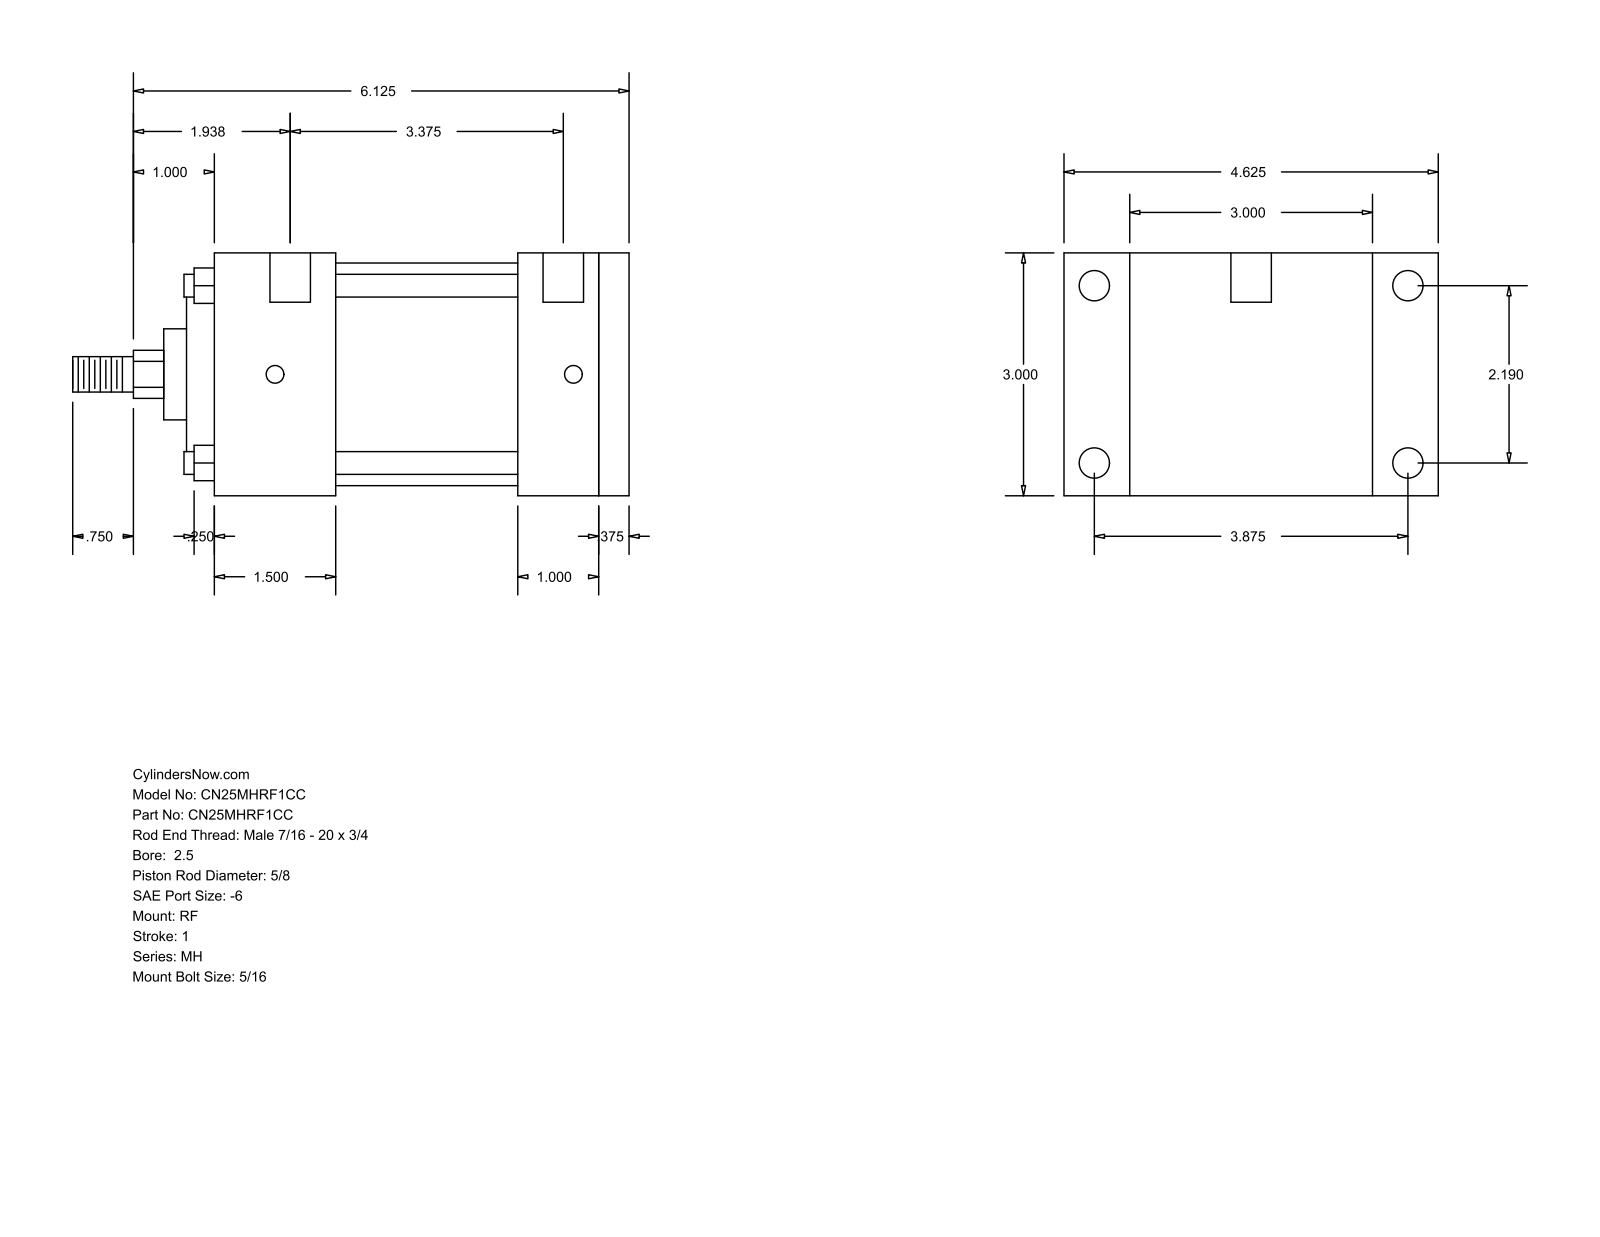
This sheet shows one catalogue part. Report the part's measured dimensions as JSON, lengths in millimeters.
{"part_name": "MH_RF__0250_0.625", "step_written_by": "GSSL Pune (CONFIG_CONTROL_DESIGN)", "units": "millimeters", "bodies": {"solids": 0, "faces": 94, "planar": 65, "cylindrical": 29, "other": 0}, "overall_size": [174.62, 117.47, 76.2], "round_holes": [[5.56, 4], [9.53, 4], [12.7, 2]], "round_bosses_or_shafts": [[7.14, 4], [69.85, 1], [55.55, 1], [28.57, 1], [15.88, 1], [11.11, 1]], "partial_cylinders_radius": [[7.54, 1]], "face_to_face_distances": [76.2, 9.52, 130.17, 120.65, 25.4, 38.1, 82.55, 57.15, 95.25, 34.92], "hole_center_spacings": [55.62, 93.66, 98.42, 113.05, 3.17, 4.76, 85.73, 88.9]}
